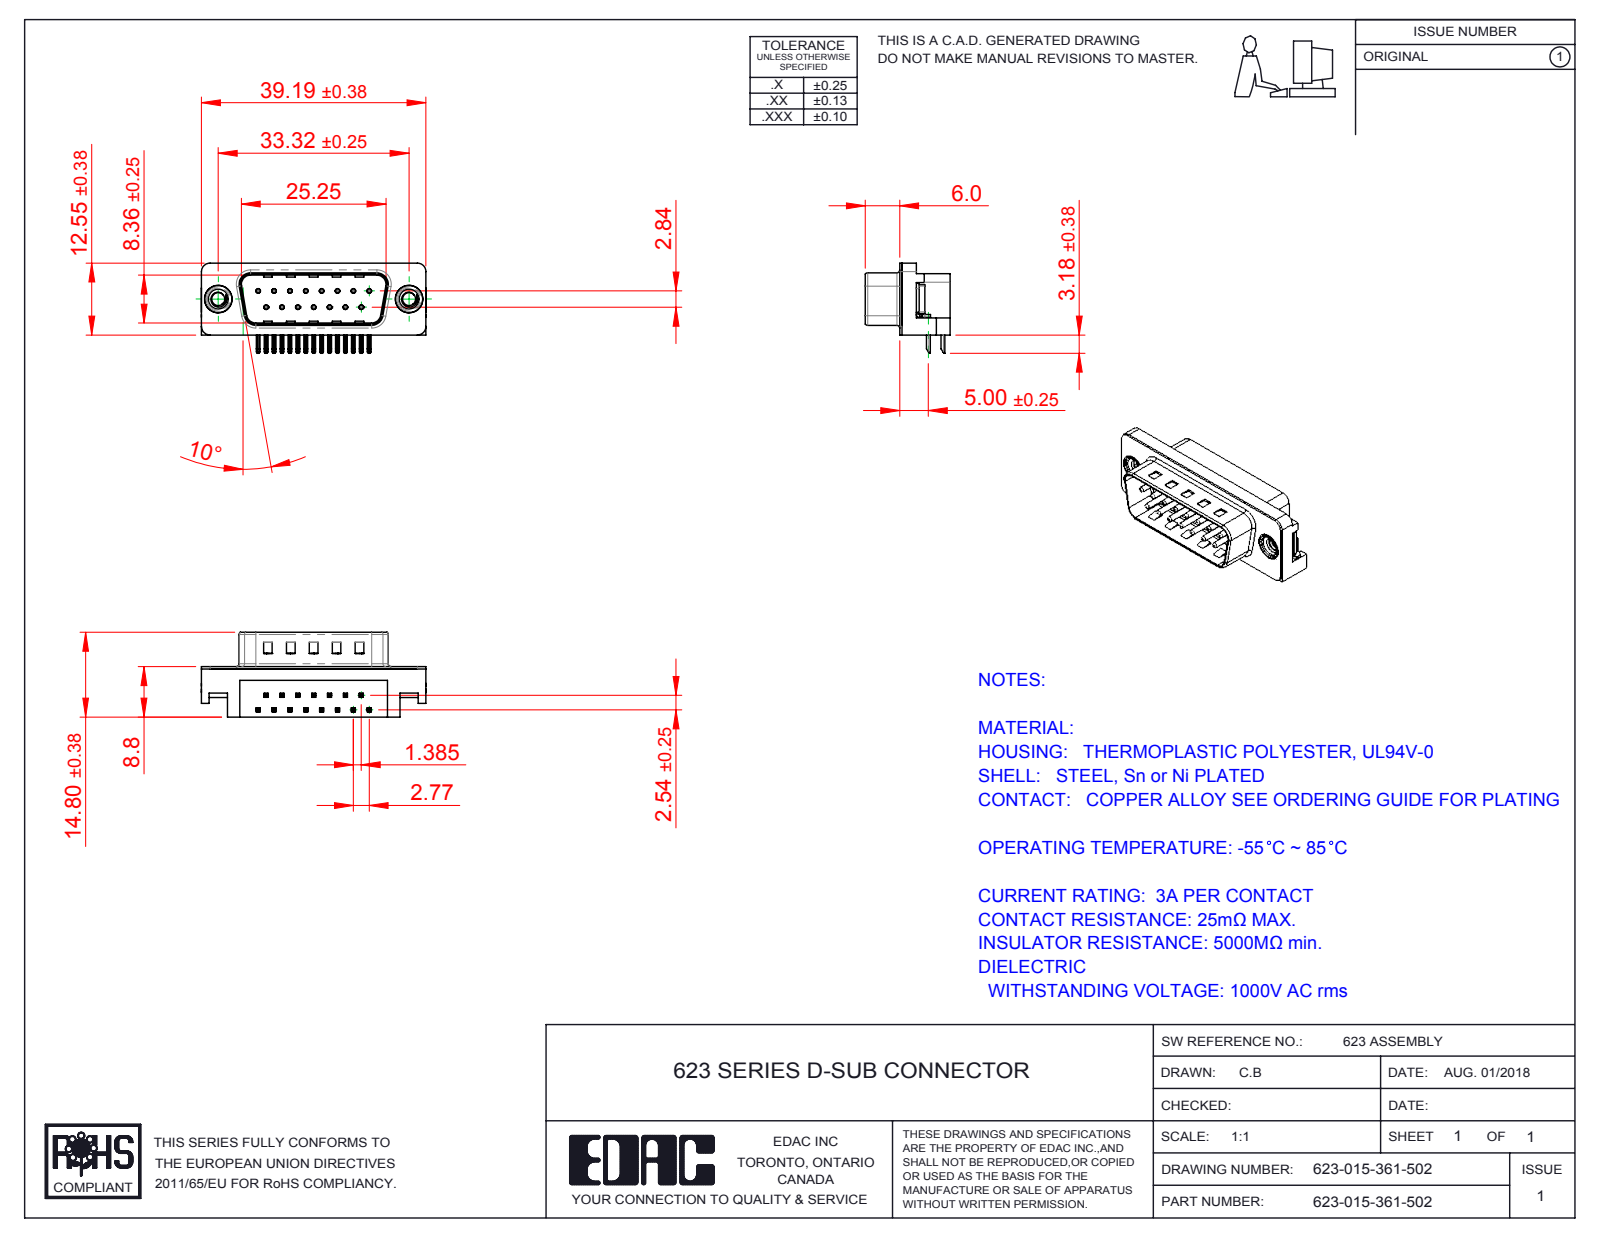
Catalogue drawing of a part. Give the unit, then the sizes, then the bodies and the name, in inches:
Units: inches
Overall size (bounding box): 1.544 × 0.619 × 0.583
Round holes (diameter × count): ⌀0.014 ×15, ⌀0.031 ×15, ⌀0.089 ×2, ⌀0.157 ×2, ⌀0.189 ×2, ⌀0.197 ×2
Round bosses / shafts (diameter × count): ⌀0.03 ×15, ⌀0.193 ×2, ⌀0.187 ×2, ⌀0.154 ×2
Partial cylindrical surfaces — rounded edges, fillets, slot ends (radius × count): R0.01 ×68, R0.005 ×30, R0.039 ×16, R0.02 ×9, R0.059 ×6, R0.035 ×4, R0.063 ×4, R0.079 ×4
Main face-to-face distances: 0.016, 0.331, 0.083, 0.067, 0.412, 0.346, 0.428, 0.345, 0.232, 0.114
Hole centre spacings: 0.124, 0.109, 0.218, 0.327, 0.436, 0.198, 0.198, 0.294
Volume: 0.203 in³ · Surface area: 7.572 in²
Bodies: 21 solids, 1467 faces (893 planar, 435 cylindrical, 139 other)
Part name (STEP PRODUCT): 623 Shell_15 Socket; 623 Contact Bottom; 623 Non Board Mount; 623 Contact Top (+3 more)
STEP written by: SolidWorks 2016 (CONFIG_CONTROL_DESIGN)
